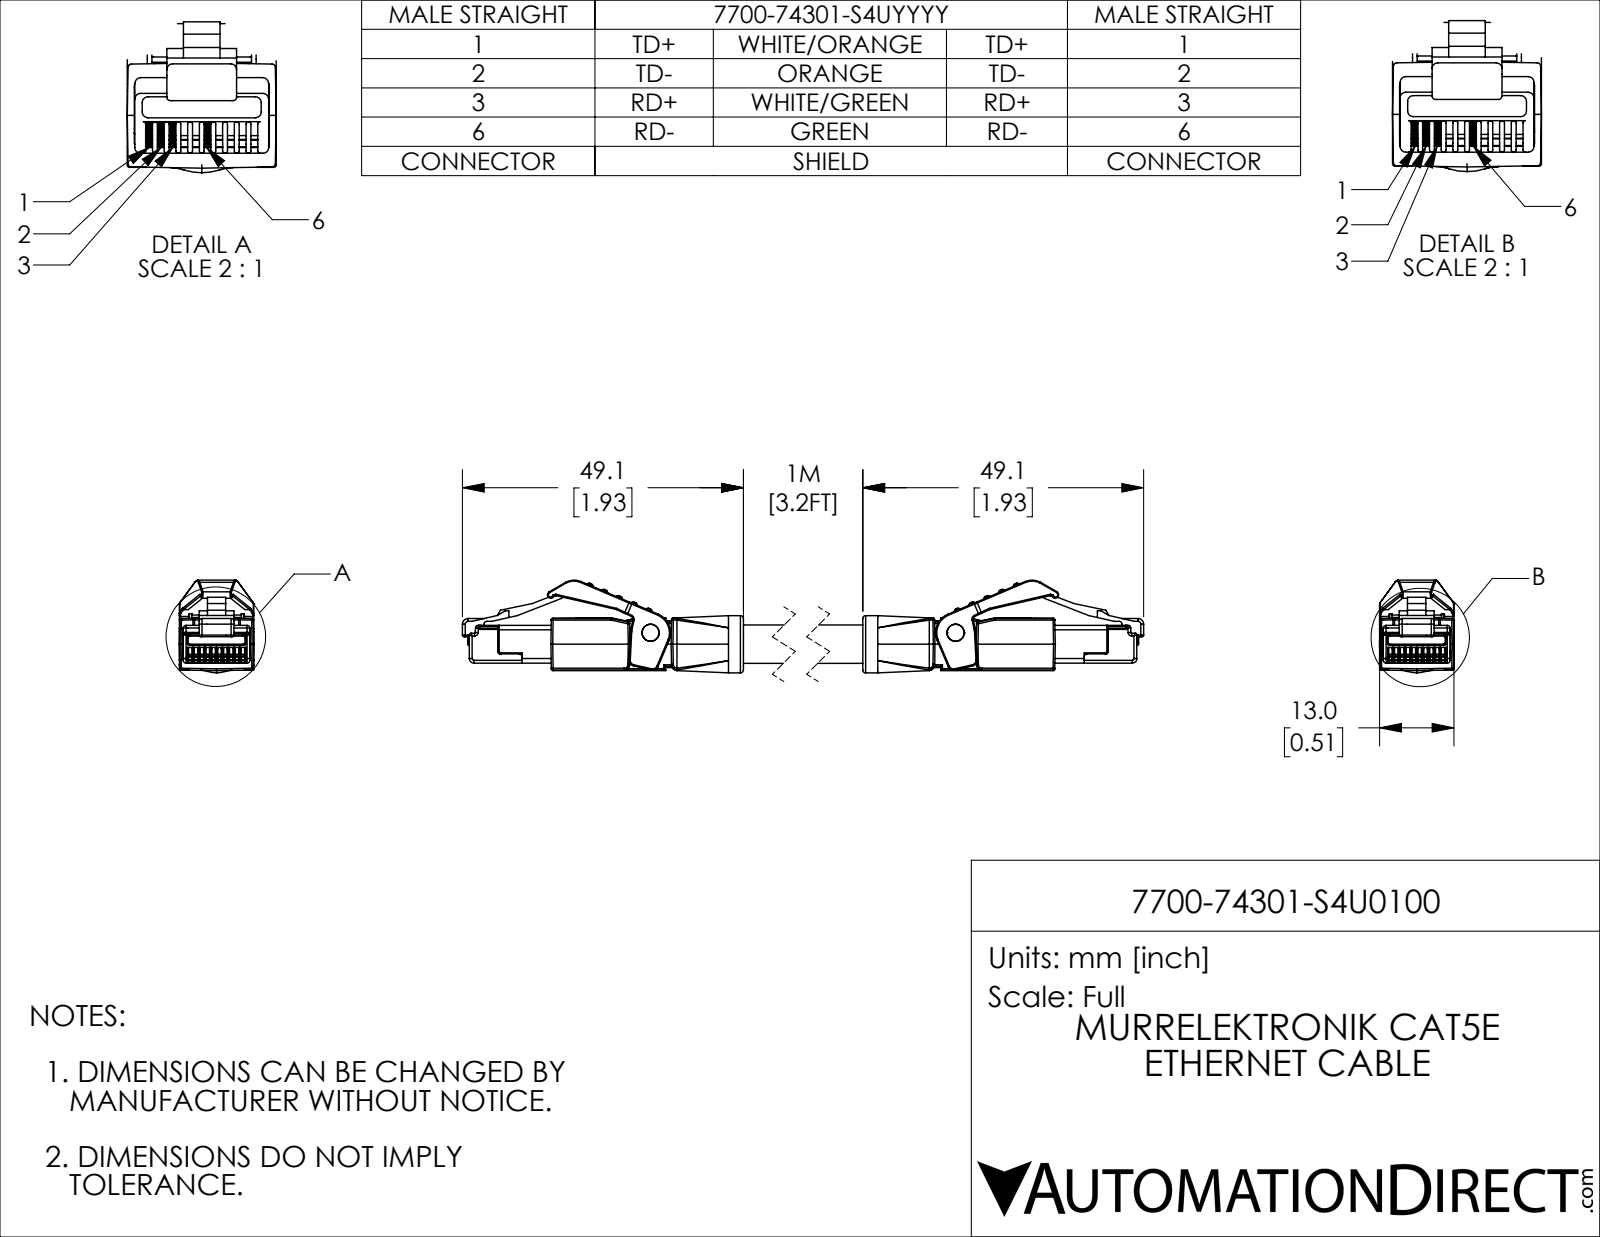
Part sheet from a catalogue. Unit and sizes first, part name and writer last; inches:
Units: inches
Overall size (bounding box): 5.112 × 0.638 × 0.512
Round holes (diameter × count): ⌀0.118 ×2
Round bosses / shafts (diameter × count): ⌀0.117 ×2, ⌀0.394 ×1, ⌀0.264 ×1
Partial cylindrical surfaces — rounded edges, fillets, slot ends (radius × count): R0.008 ×136, R0.012 ×114, R0.004 ×40, R0.02 ×36, R0.039 ×10, R0.031 ×6, R0.079 ×4, R0.197 ×4
Main face-to-face distances: 0.512, 0.362, 0.024, 0.488, 0.026, 0.26, 0.069, 0.443, 0.045, 0.419
Hole centre spacings: 2.526
Volume: 0.668 in³ · Surface area: 10.82 in²
Bodies: 2 solids, 1406 faces (568 planar, 566 cylindrical, 272 other)
Part name (STEP PRODUCT): 7700-74301-S4U0100_1; 7700-74301-S4U0100
STEP written by: SolidWorks 2021 (CONFIG_CONTROL_DESIGN)
